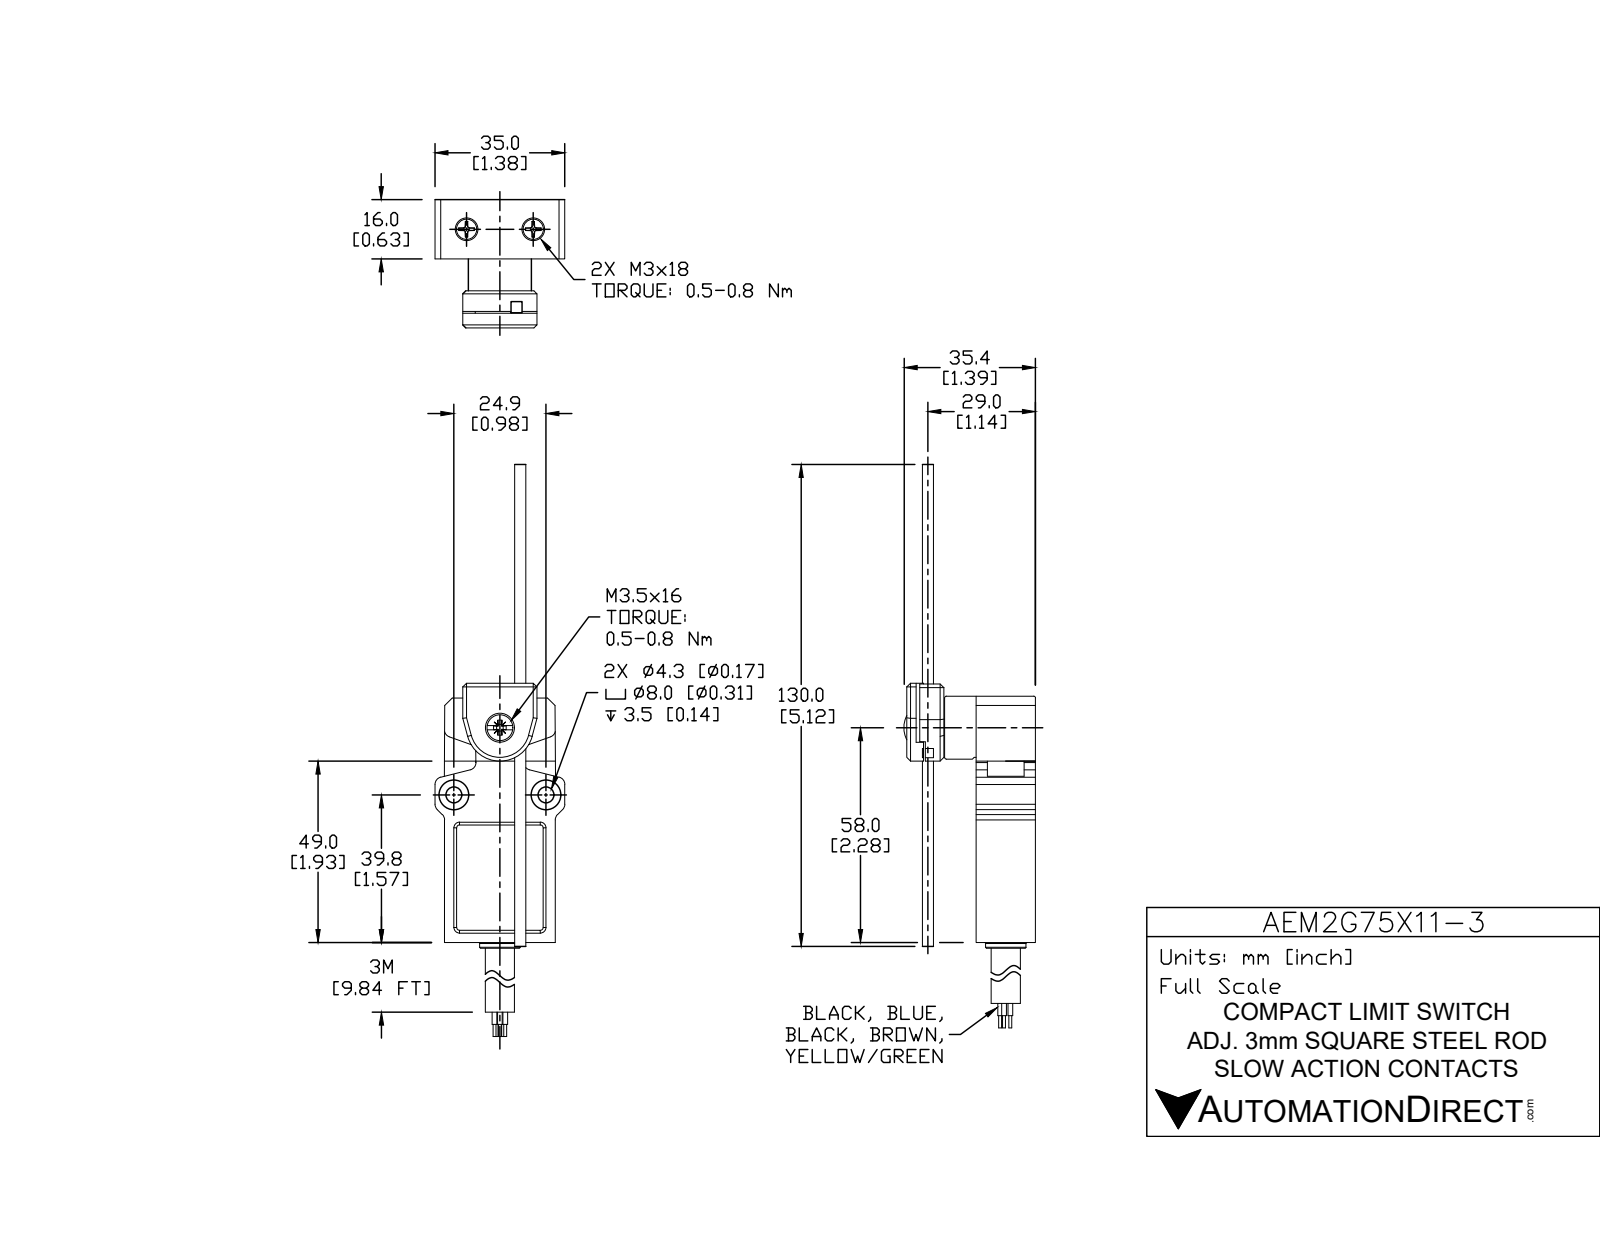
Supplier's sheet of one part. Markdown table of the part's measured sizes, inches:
| quantity | value |
| --- | --- |
| part name | AEM2G75X11-3 |
| STEP written by | SolidWorks 2017 (AUTOMOTIVE_DESIGN) |
| units | inches |
| bodies | 7 solids, 223 faces (145 planar, 63 cylindrical, 15 other) |
| overall size | 6.854 × 1.87 × 1.366 |
| volume | 1.965 in³ |
| surface area | 21.2 in² |
| round holes (diameter × count) | 0.118 × 2, 0.173 × 2, 0.323 × 2, 0.138 × 1, 0.197 × 1, 0.315 × 1 |
| round bosses / shafts (diameter × count) | 0.622 × 1, 0.323 × 1, 0.276 × 1 |
| partial cylindrical surfaces (radius × count) | 0.079 × 8, 0.059 × 2, 0.173 × 1, 0.256 × 1, 0.26 × 1, 0.354 × 1 |
| main face-to-face distances | 0.63, 0.118, 1.098, 0.587, 1.181, 0.469, 1.217, 0.313, 0.868, 0.11 |
| hole center spacings | 0.863, 0.748, 0.984 |
